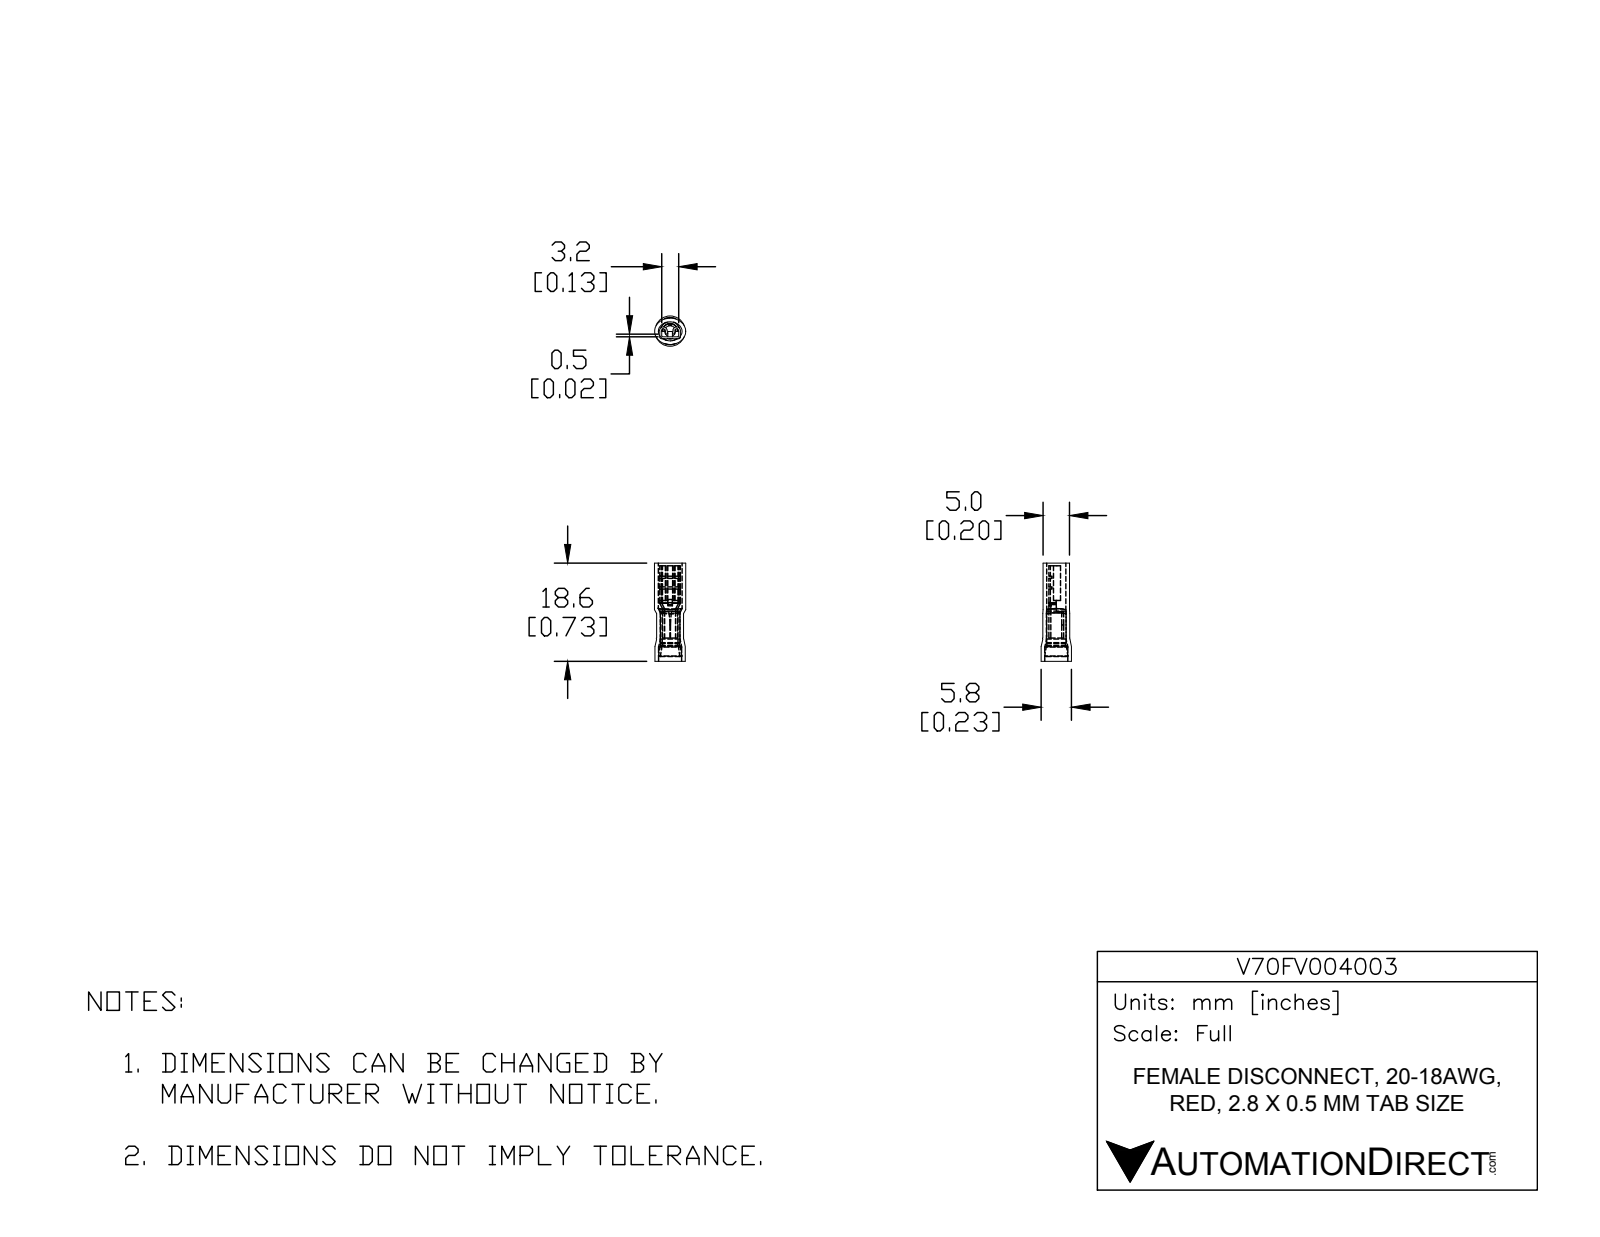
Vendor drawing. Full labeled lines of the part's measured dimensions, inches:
Part name (STEP PRODUCT): V70FV004003
STEP written by: SolidWorks 2017 (AUTOMOTIVE_DESIGN)
Units: inches
Bodies: 3 solids, 127 faces (51 planar, 36 cylindrical, 40 other)
Overall size (bounding box): 0.732 × 0.232 × 0.226
Volume: 0.016 in³ · Surface area: 1.584 in²
Round holes (diameter × count): ⌀0.082 ×1, ⌀0.117 ×1, ⌀0.146 ×1, ⌀0.171 ×1
Round bosses / shafts (diameter × count): ⌀0.226 ×1, ⌀0.201 ×1, ⌀0.145 ×1, ⌀0.109 ×1
Partial cylindrical surfaces — rounded edges, fillets, slot ends (radius × count): R0.005 ×2, R0.01 ×2, R0.013 ×2, R0.027 ×2, R0.619 ×2, R0.013 ×1, R0.027 ×1
Main face-to-face distances: 0.014, 0.14, 0.732, 0.154, 0.126, 0.079, 0.173, 0.539, 0.713, 0.02
